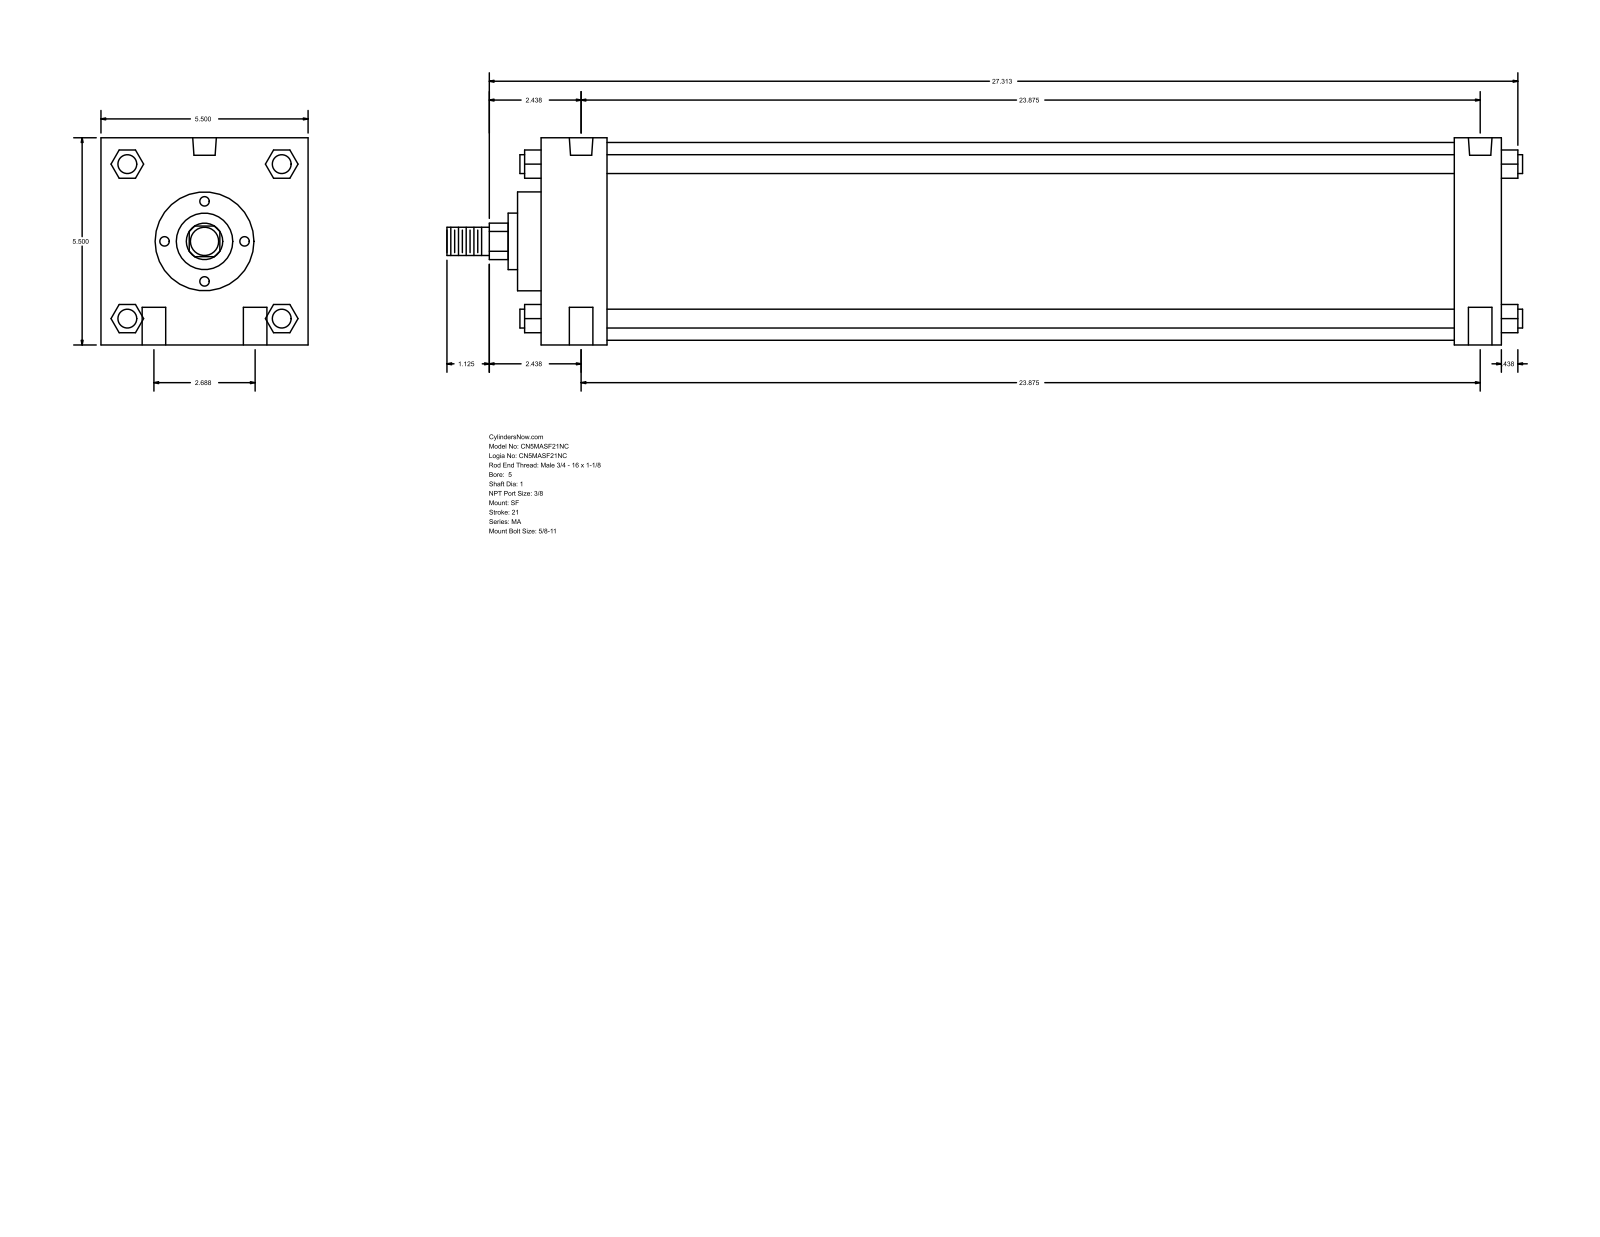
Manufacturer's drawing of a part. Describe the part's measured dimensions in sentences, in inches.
The part is named "MA_SF__0500_1". Its 3-D file was written by "GSSL Pune (CONFIG_CONTROL_DESIGN)". It is 0 solids with 126 faces: 95 planar, 31 cylindrical and 0 other. Overall it measures 28.563 by 5.5 by 5.5 inches. Round holes: 4 of diameter 0.625, 2 of diameter 0.437, 2 of diameter 0.627. Round bosses or shafts: 4 of diameter 0.5, 1 of diameter 5.25, 1 of diameter 2.625, 1 of diameter 1.5, 1 of diameter 1, 1 of diameter 0.75. Partial cylindrical surfaces (rounded edges, fillets, slot ends): 1 of radius 0.484. The main face-to-face distances are 5.5, 25.5, 1.75, 24.25, 22.5, 23.75, 1.25, 0.625, 2.375, 24.875. The hole center spacings are 1.344, 23.913, 23.875, 2.687, 24.026, 23.5.
